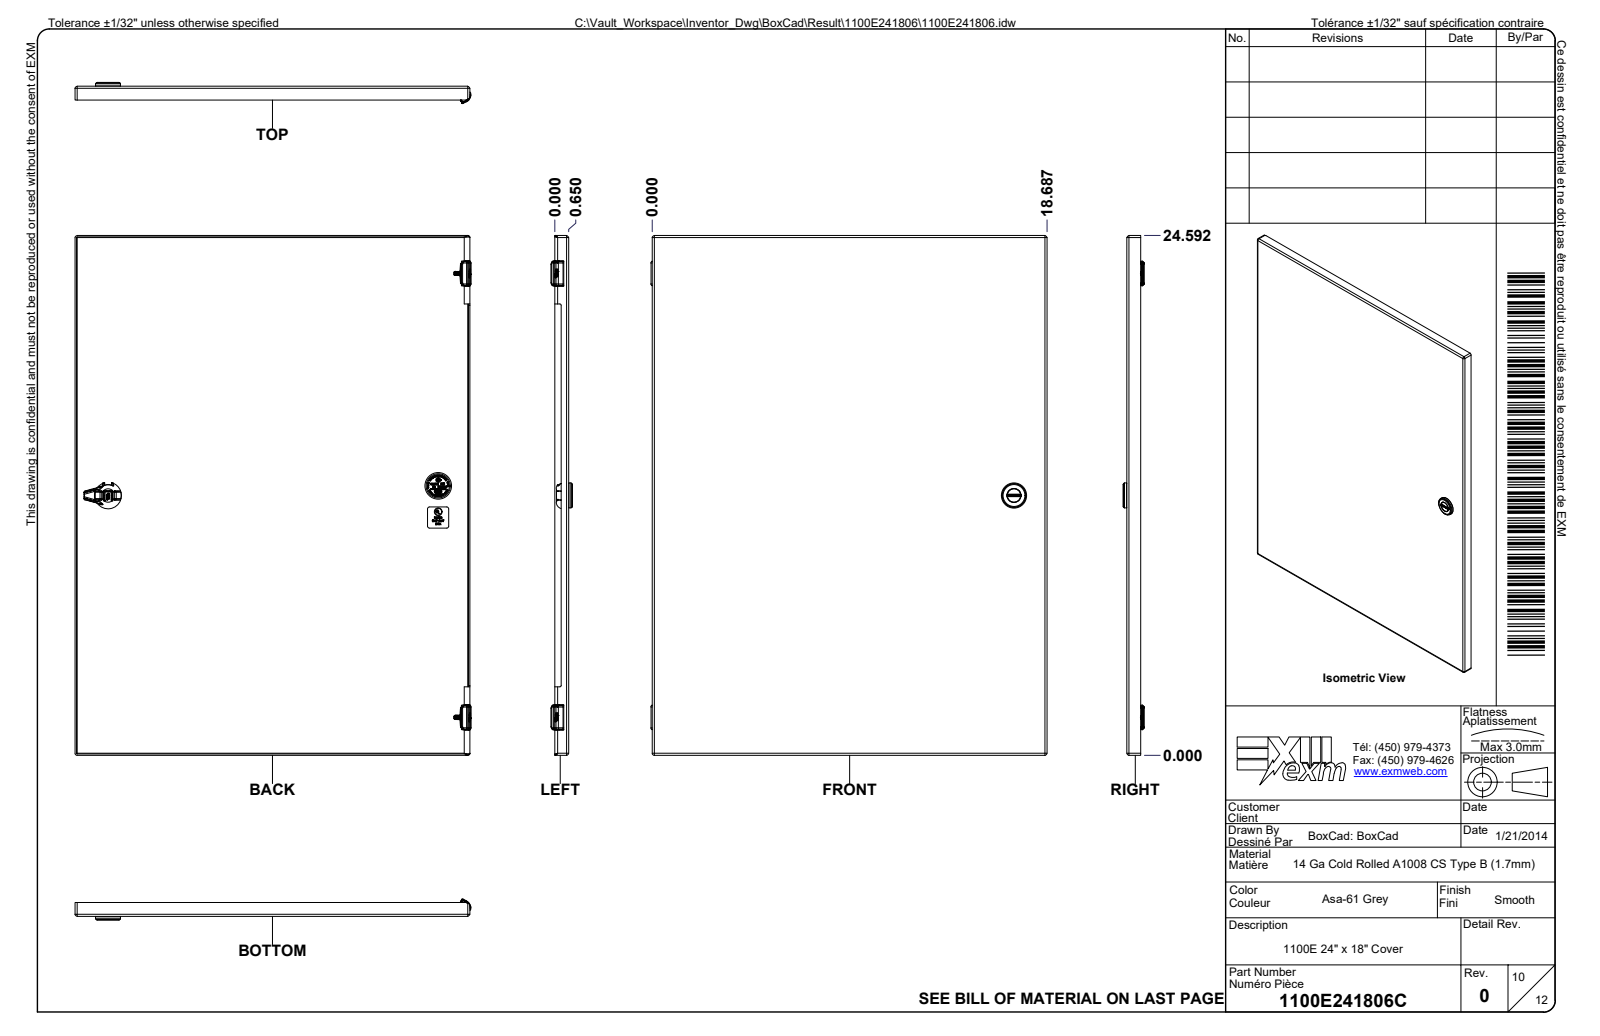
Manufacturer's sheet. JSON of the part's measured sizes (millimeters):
{"part_name": "1100E241806; 1100E241806B; 1100E241806B-P; 1100E241806C (+8 more)", "step_written_by": "Autodesk Inventor 2024 (AUTOMOTIVE_DESIGN)", "units": "millimeters", "bodies": {"solids": 14, "faces": 5792, "planar": 2597, "cylindrical": 1080, "other": 2115}, "overall_size": [624.6, 476.1, 160.4], "volume_mm3": 1658000, "surface_area_mm2": 1937000, "round_holes": [[22.2, 8], [28.6, 8], [7.4, 4], [4.4, 2], [4.5, 2], [10, 2], [0.8, 1], [1.1, 1], [3.2, 1], [5.1, 1], [9.5, 1], [27, 1]], "round_bosses_or_shafts": [[28.6, 8], [22.2, 8], [5, 3], [4.9, 2], [4, 2], [32, 1], [31.8, 1], [30, 1]], "partial_cylinders_radius": [[0.3, 238], [0.5, 126], [1, 46], [0.2, 34], [2, 29], [0.8, 22], [2.5, 22], [0.8, 20]], "face_to_face_distances": [1.7, 154.1, 155.8, 152.3, 455.5, 607.9, 457.2, 453.7, 609.6, 606.1], "hole_center_spacings": [85.7, 171.5, 27.4, 85.8, 180.1, 189.2, 251.9, 257.1]}
